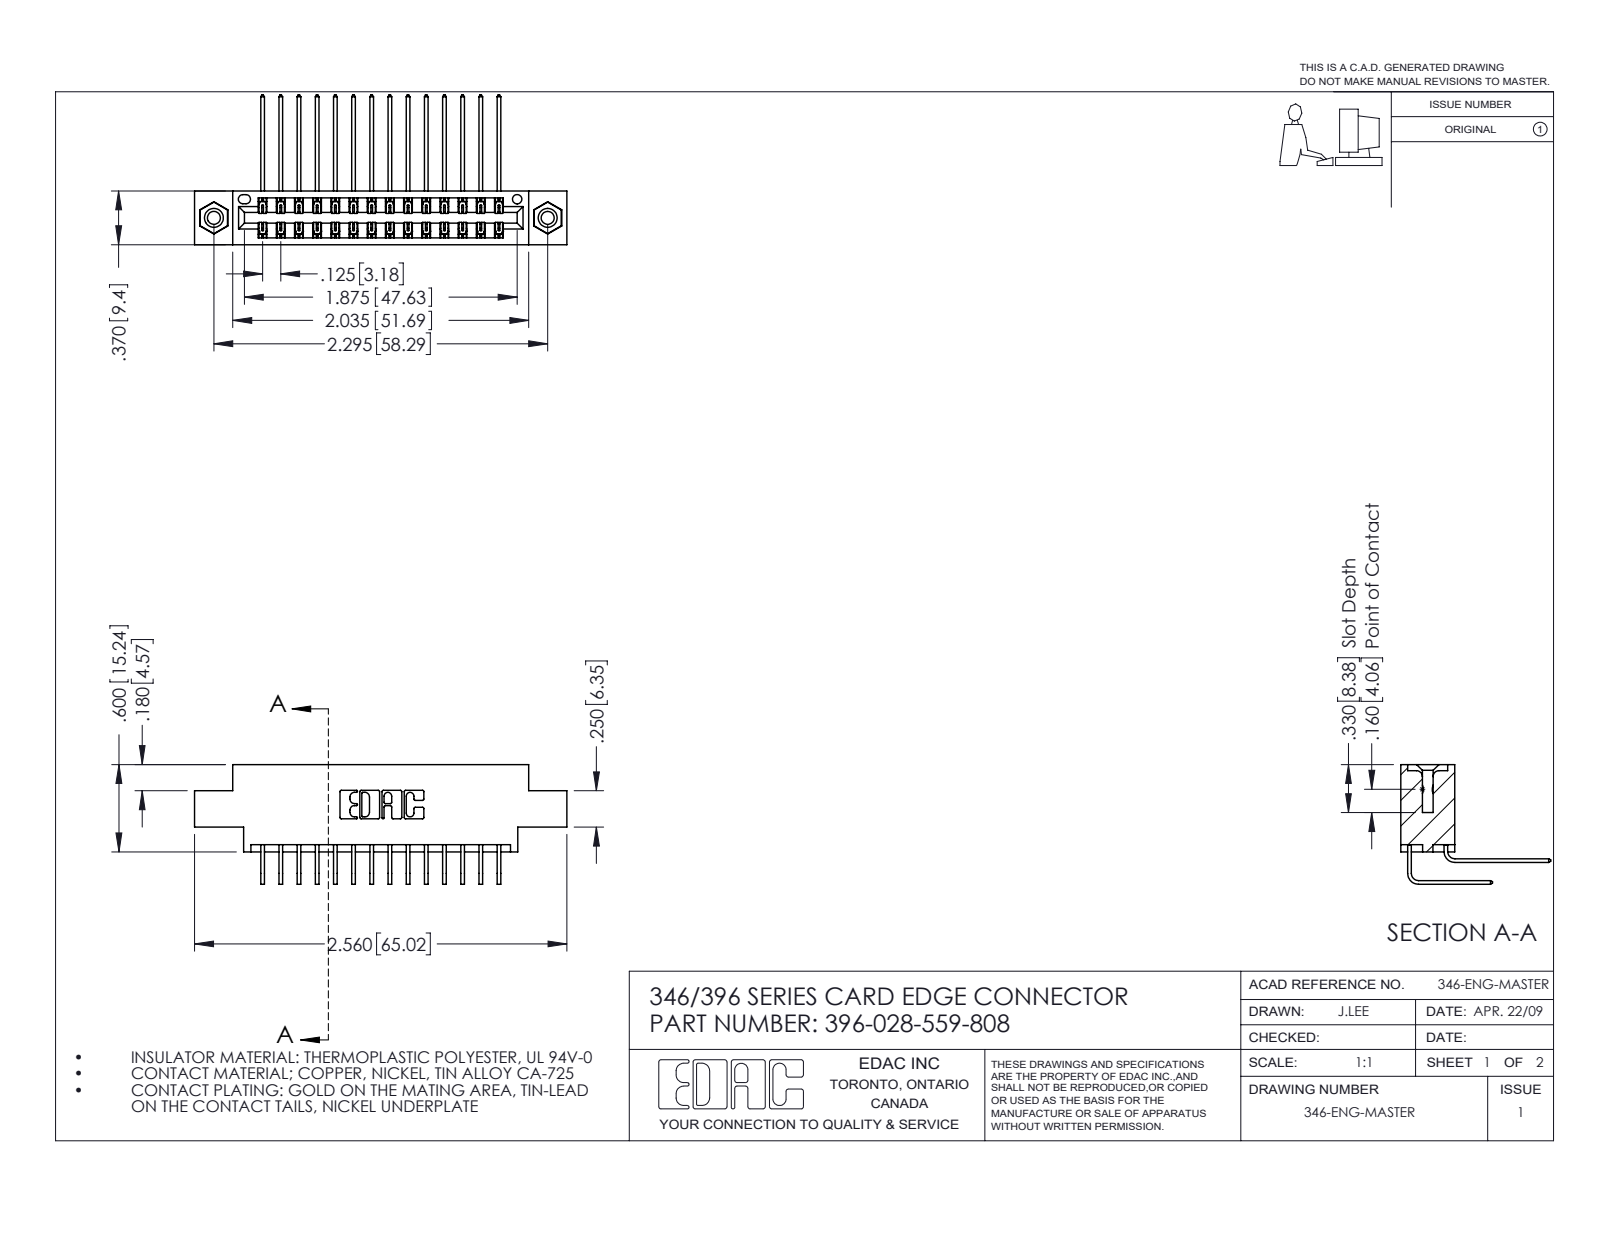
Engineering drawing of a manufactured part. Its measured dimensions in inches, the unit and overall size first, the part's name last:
Units: inches
Overall size (bounding box): 2.56 × 1.03 × 0.823
Round holes (diameter × count): ⌀0.089 ×2, ⌀0.125 ×2, ⌀0.156 ×2, ⌀0.064 ×1
Round bosses / shafts (diameter × count): ⌀0.155 ×2
Partial cylindrical surfaces — rounded edges, fillets, slot ends (radius × count): R0.006 ×42, R0.01 ×22, R0.007 ×6, R0.031 ×6, R0.026 ×3, R0.014 ×2, R0.022 ×2, R0.024 ×2
Main face-to-face distances: 0.048, 0.322, 0.37, 0.25, 0.025, 0.072, 0.298, 0.222, 0.275, 0.148
Hole centre spacings: 0.246, 2.089, 2.295
Volume: 0.374 in³ · Surface area: 13.88 in²
Bodies: 31 solids, 1698 faces (1148 planar, 534 cylindrical, 16 other)
Part name (STEP PRODUCT): 346 Part_0.170 Offset - 0.156 Dia-TI; 345-250-001_345-250-003-102; 396-028-559-808; 345-292-001_559 Tail - 2 (+1 more)
STEP written by: SolidWorks 2016 (CONFIG_CONTROL_DESIGN)
